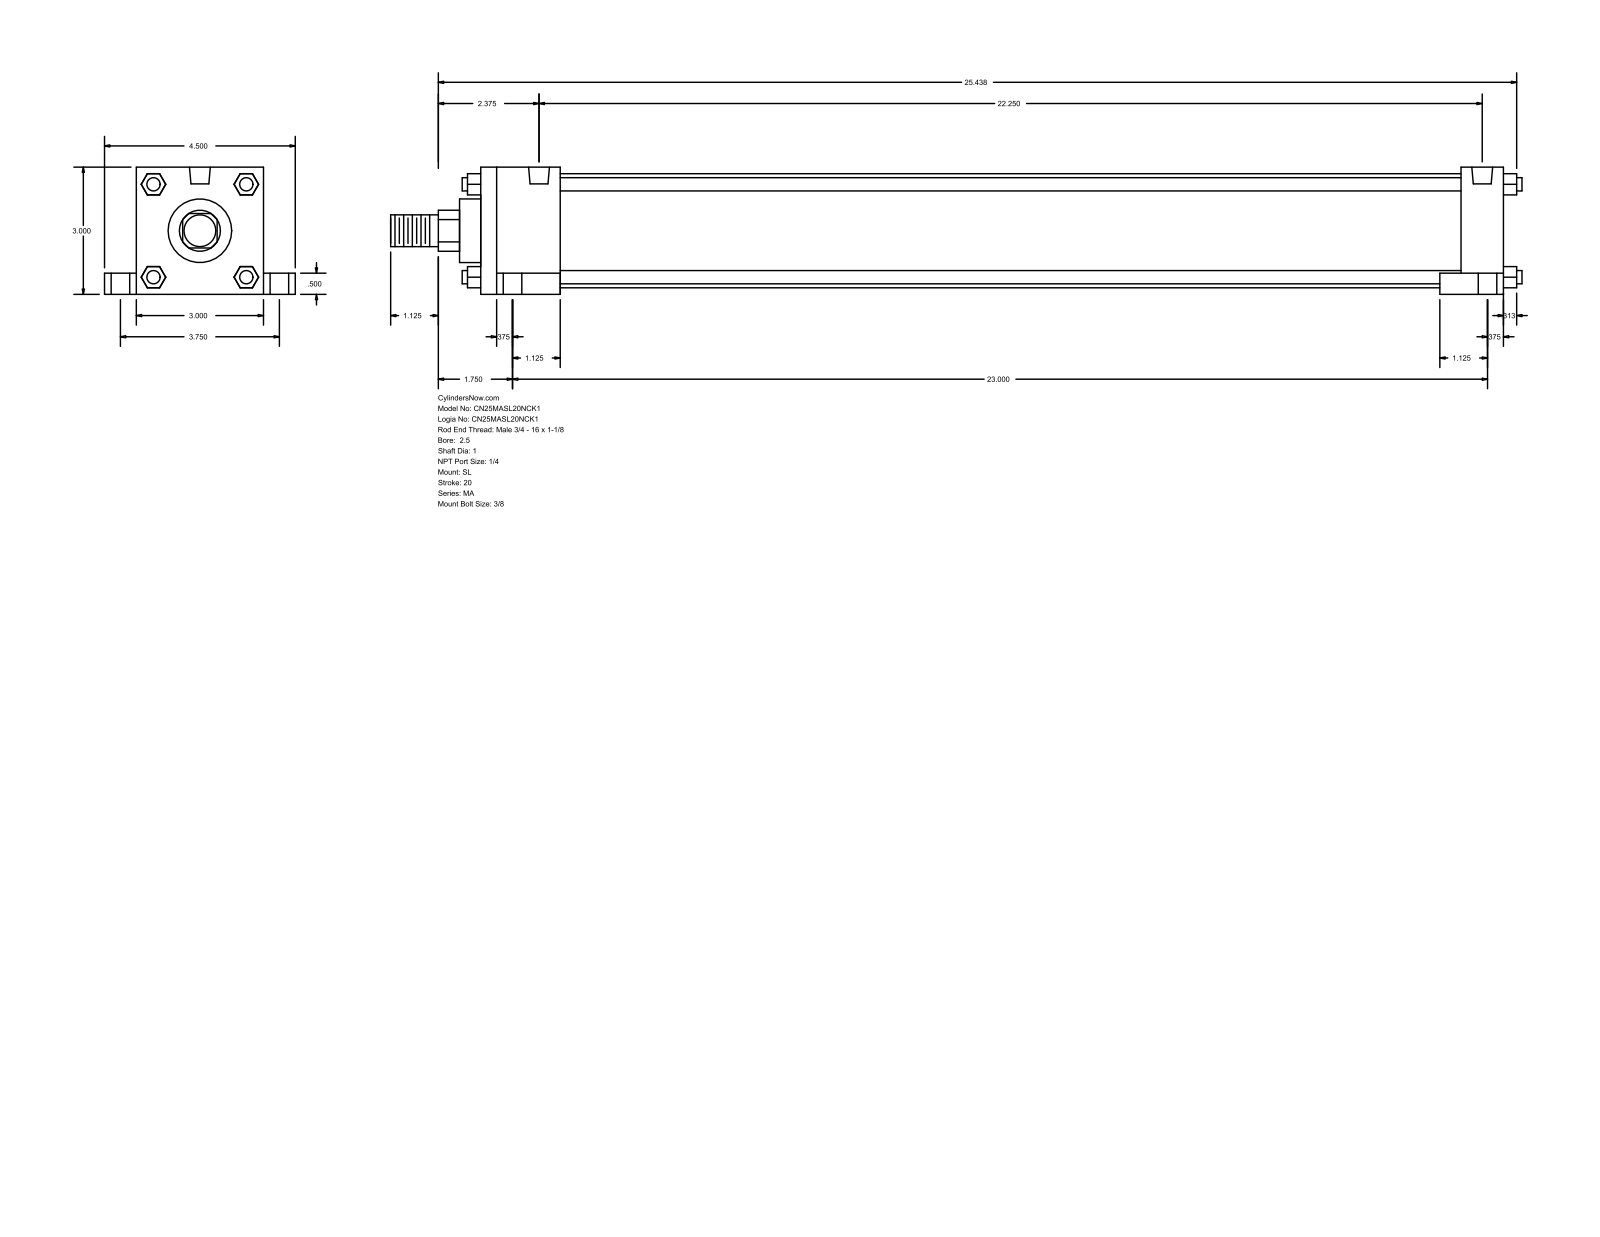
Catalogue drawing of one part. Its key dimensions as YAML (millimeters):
part_name: "MA_SL__0250_1"
step_written_by: "GSSL Pune (CONFIG_CONTROL_DESIGN)"
units: millimeters
bodies: {solids: 0, faces: 148, planar: 112, cylindrical: 36, other: 0}
overall_size: [677.86, 114.3, 76.2]
round_holes:
  - {diameter: 7.94, count: 4}
  - {diameter: 11.11, count: 4}
  - {diameter: 17.46, count: 4}
  - {diameter: 12.49, count: 2}
round_bosses_or_shafts:
  - {diameter: 7.94, count: 4}
  - {diameter: 68.33, count: 1}
  - {diameter: 38.1, count: 1}
  - {diameter: 25.4, count: 1}
  - {diameter: 19.05, count: 1}
partial_cylinders:
  - {radius: 12.29, count: 1}
face_to_face_distances: [76.2, 612.77, 12.7, 25.4, 47.63, 565.14, 587.37, 539.74, 19.05, 95.25]
hole_center_spacings: [47.73, 50.2, 95.24, 565.15, 570.31, 582.98, 584.2, 591.91]
